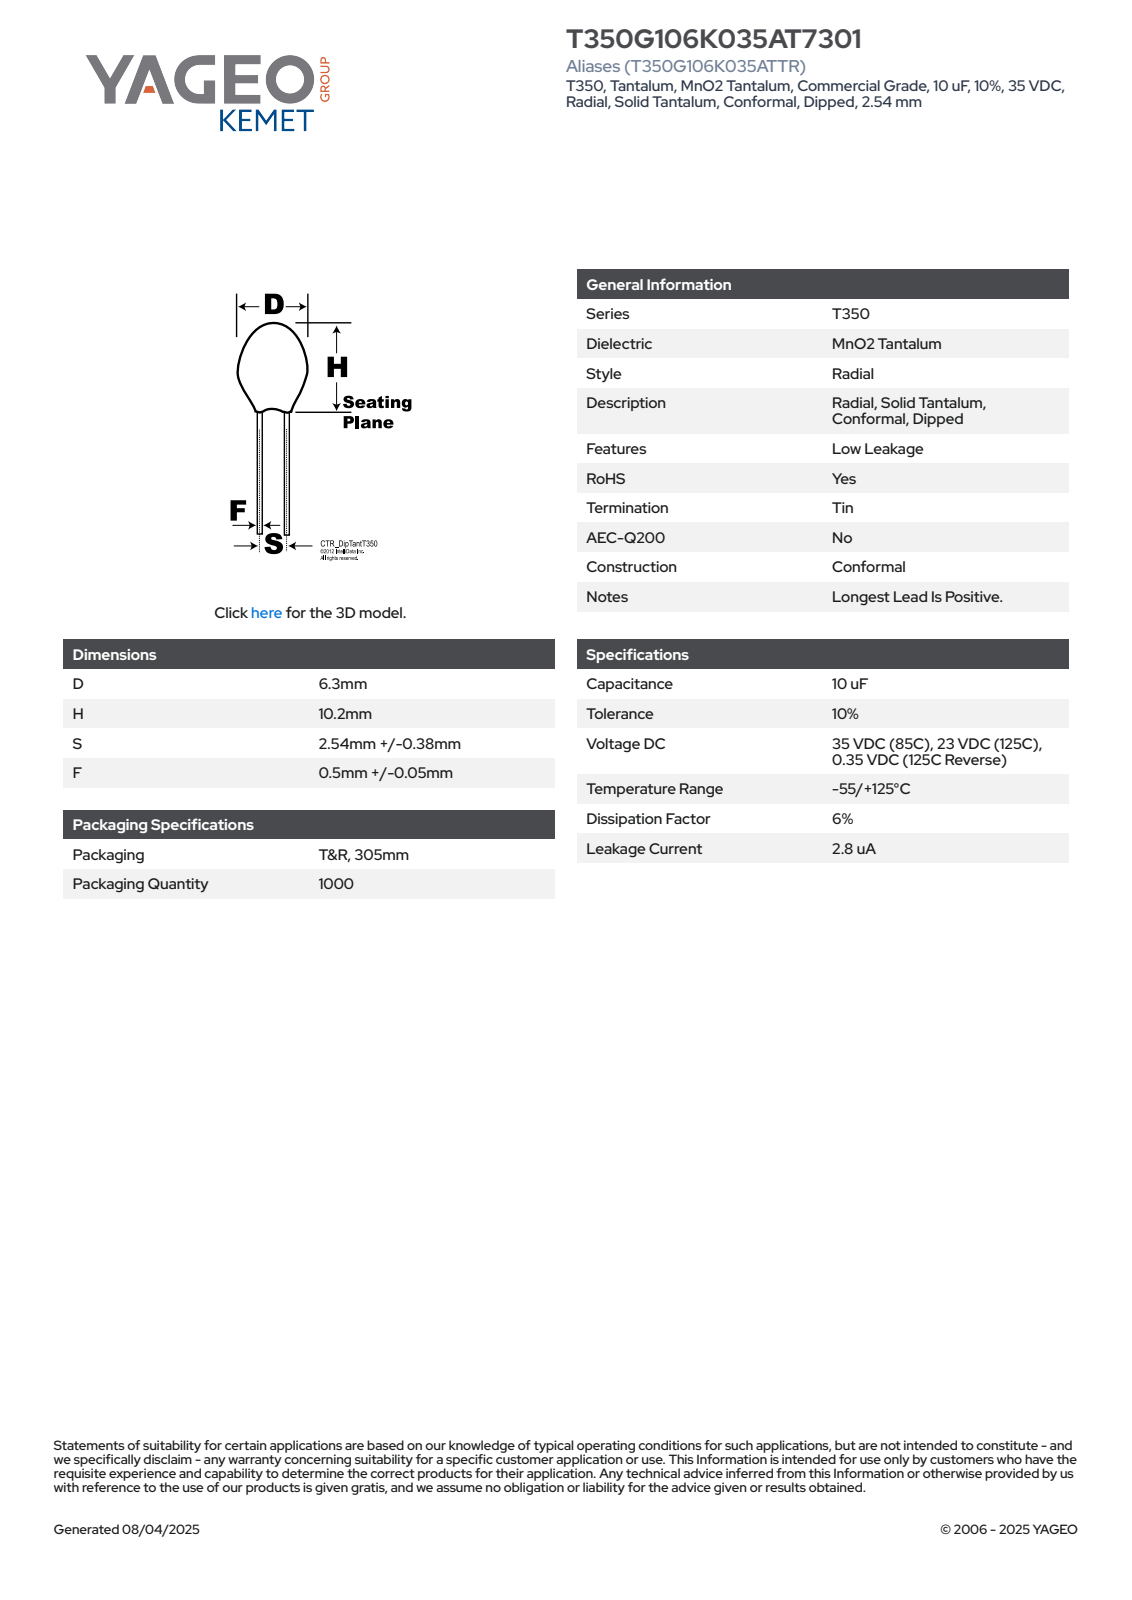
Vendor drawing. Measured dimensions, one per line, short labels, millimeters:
name: CTR_T350_D6.3H10.2S2.54LL13.96F0.55
written by: SolidWorks 2014 (AUTOMOTIVE_DESIGN)
unit: mm
bodies: 1 solid, 72 faces (26 planar, 9 cylindrical, 37 other)
size: 24.16 × 6.3 × 6.3
volume: 270 mm³; area: 263 mm²
bosses: 2× ⌀0.55, 1× ⌀6.3
rounds: 1× R3.14
face distances: 10.2, 13.96, 24.16, 19.67, 5.71, 4.49, 18.56, 4.6, 1.11, 5.6
